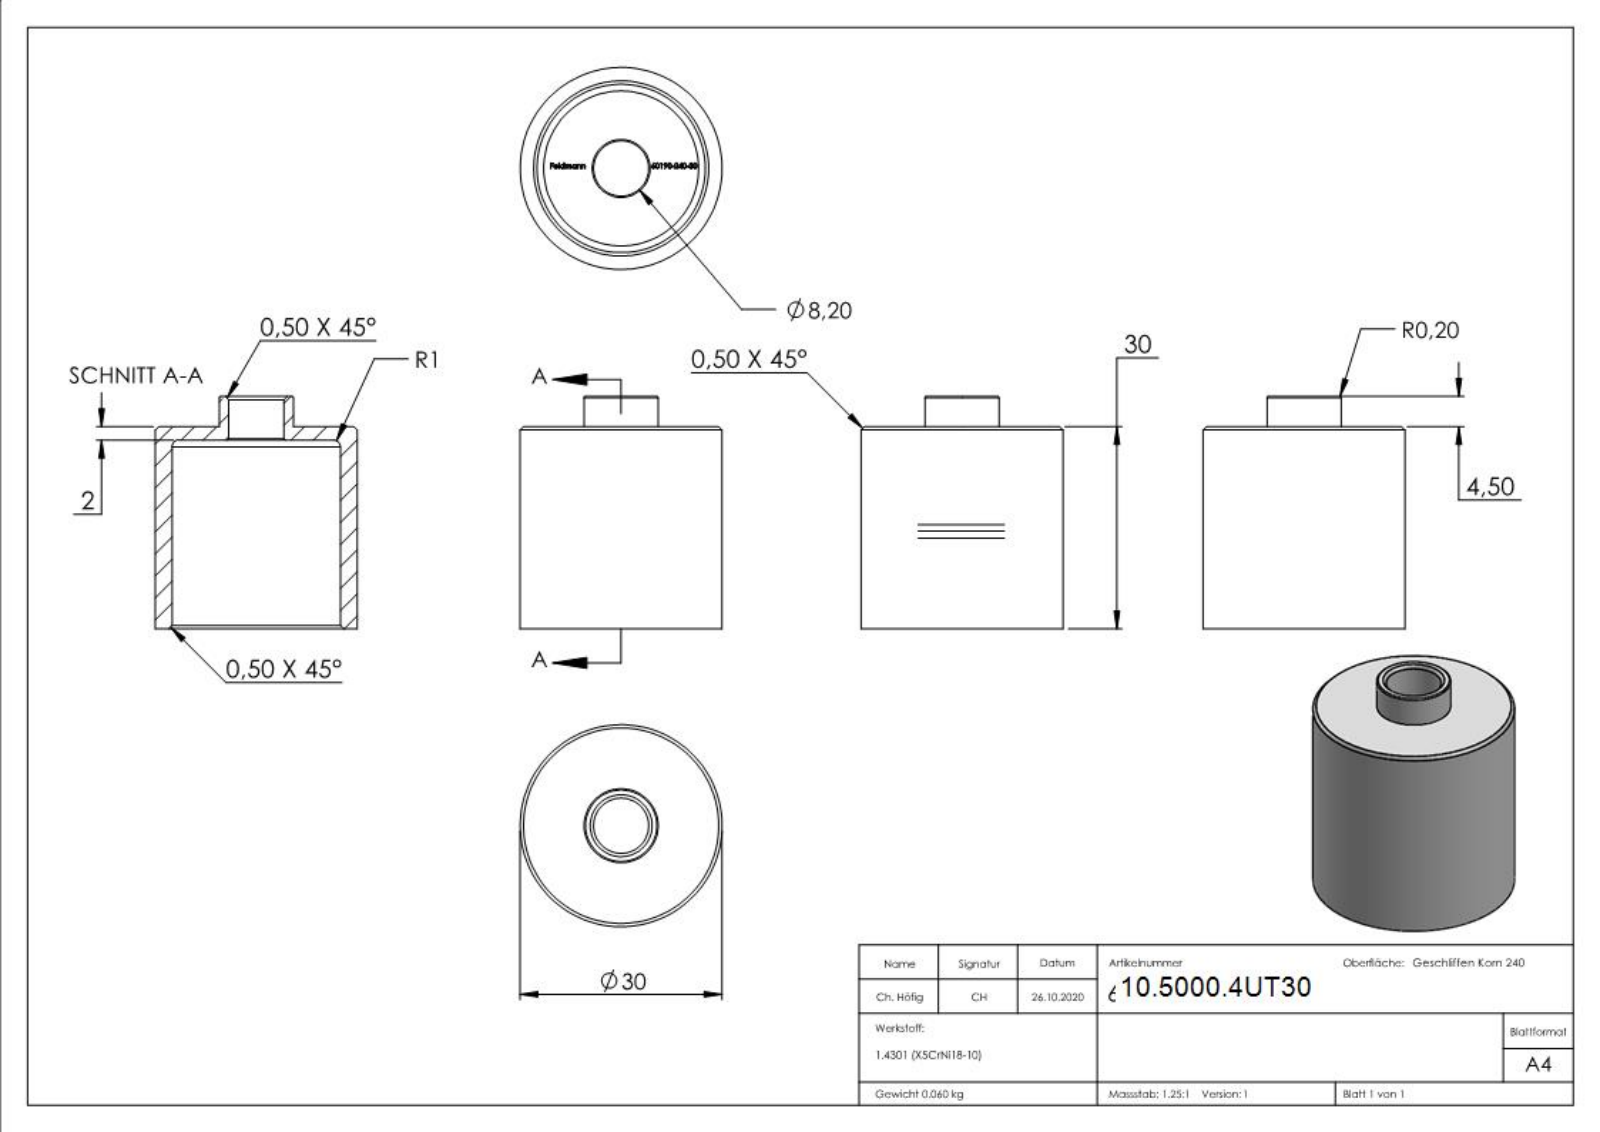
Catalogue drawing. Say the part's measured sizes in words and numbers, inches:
The part is named "60190-240-30". Its 3-D file was written by "SolidWorks 2018 (CONFIG_CONTROL_DESIGN)". It is 1 solid with 272 faces: 130 planar, 8 cylindrical and 134 other. Overall it measures 1.358 by 1.181 by 1.181 inches. Its volume is 0.46 cubic inches and its surface area 10.18 square inches. Round holes: 1 of diameter 0.323, 1 of diameter 0.984. Round bosses or shafts: 1 of diameter 1.181, 1 of diameter 0.433. The main face-to-face distances are 0.079, 1.102, 1.181, 1.358, 0.256, 0.177, 1.106, 0.075, 0.252, 0.07.
